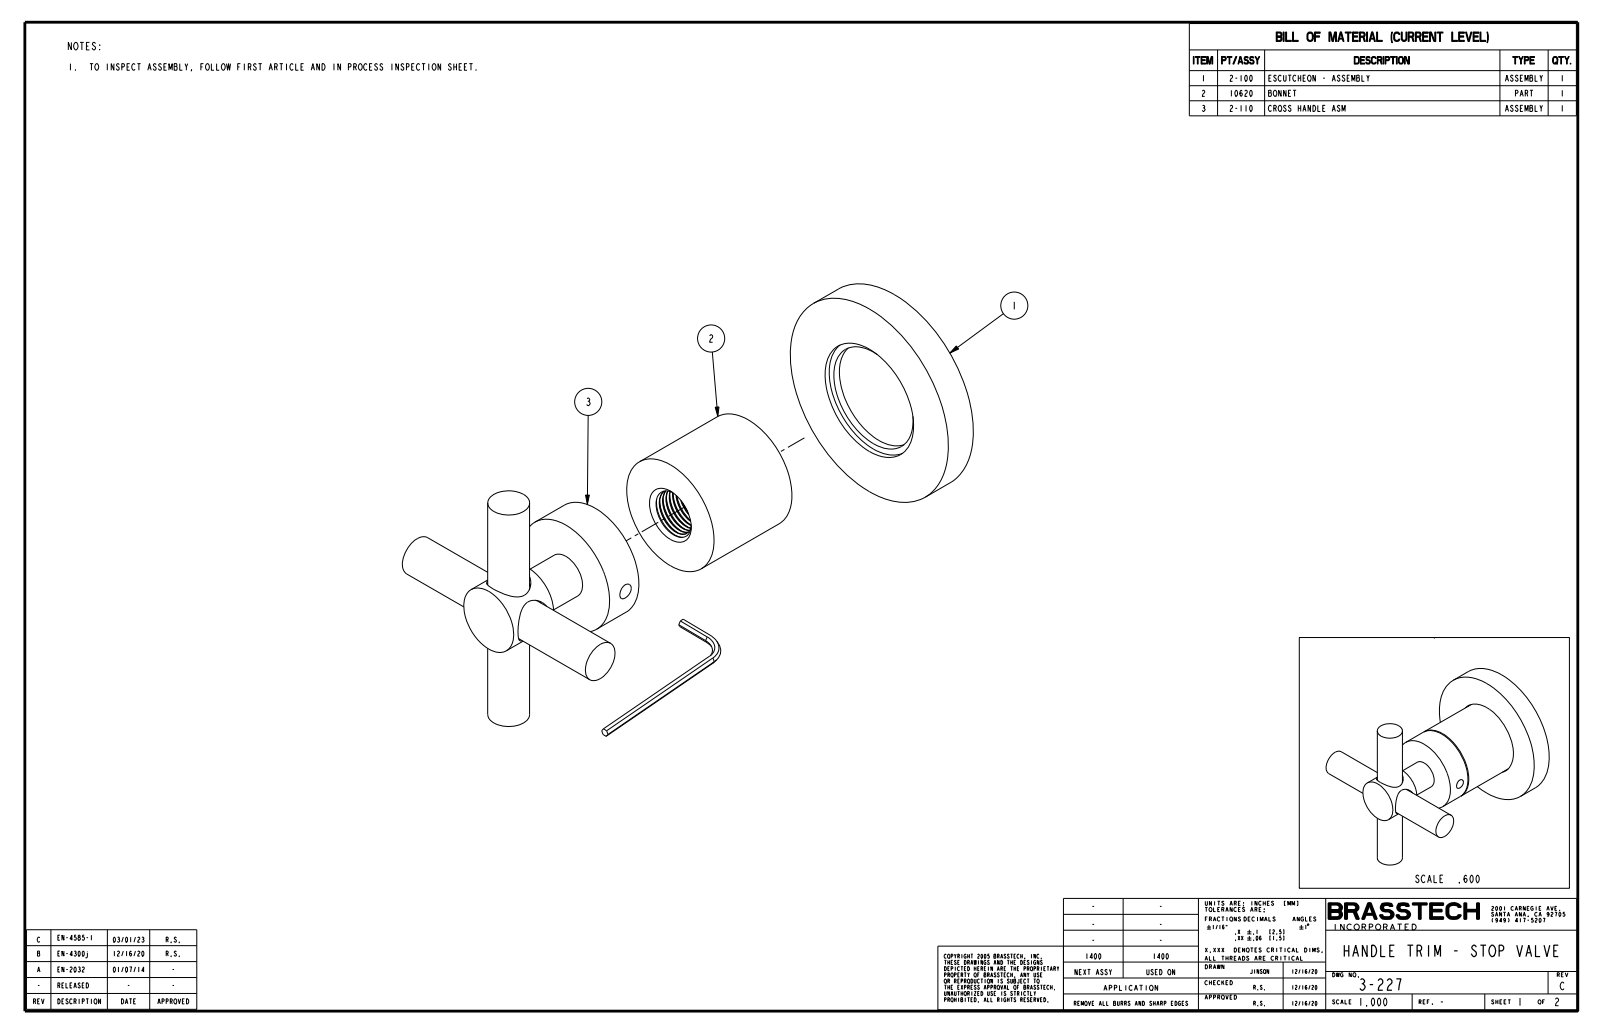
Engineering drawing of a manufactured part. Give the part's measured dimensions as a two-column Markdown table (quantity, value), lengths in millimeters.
| quantity | value |
| --- | --- |
| part name | 3-227 |
| STEP written by | CREO PARAMETRIC BY PTC INC, 2018400 (CONFIG_CONTROL_DESIGN) |
| units | millimeters |
| bodies | 1 solid, 37 faces (13 planar, 24 cylindrical, 0 other) |
| overall size | 78.8 × 69.9 × 69.9 |
| volume | 78 070 mm³ |
| surface area | 18 980 mm² |
| round holes (diameter × count) | 11.9 × 1 |
| round bosses / shafts (diameter × count) | 11.3 × 2, 60.3 × 1, 33.4 × 1, 19.1 × 1, 12.7 × 1, 10.2 × 1 |
| main face-to-face distances | 9.5, 37.7, 38.2, 28.1, 28.7, 0.5, 49.4, 39.8, 11.7, 11.2 |
